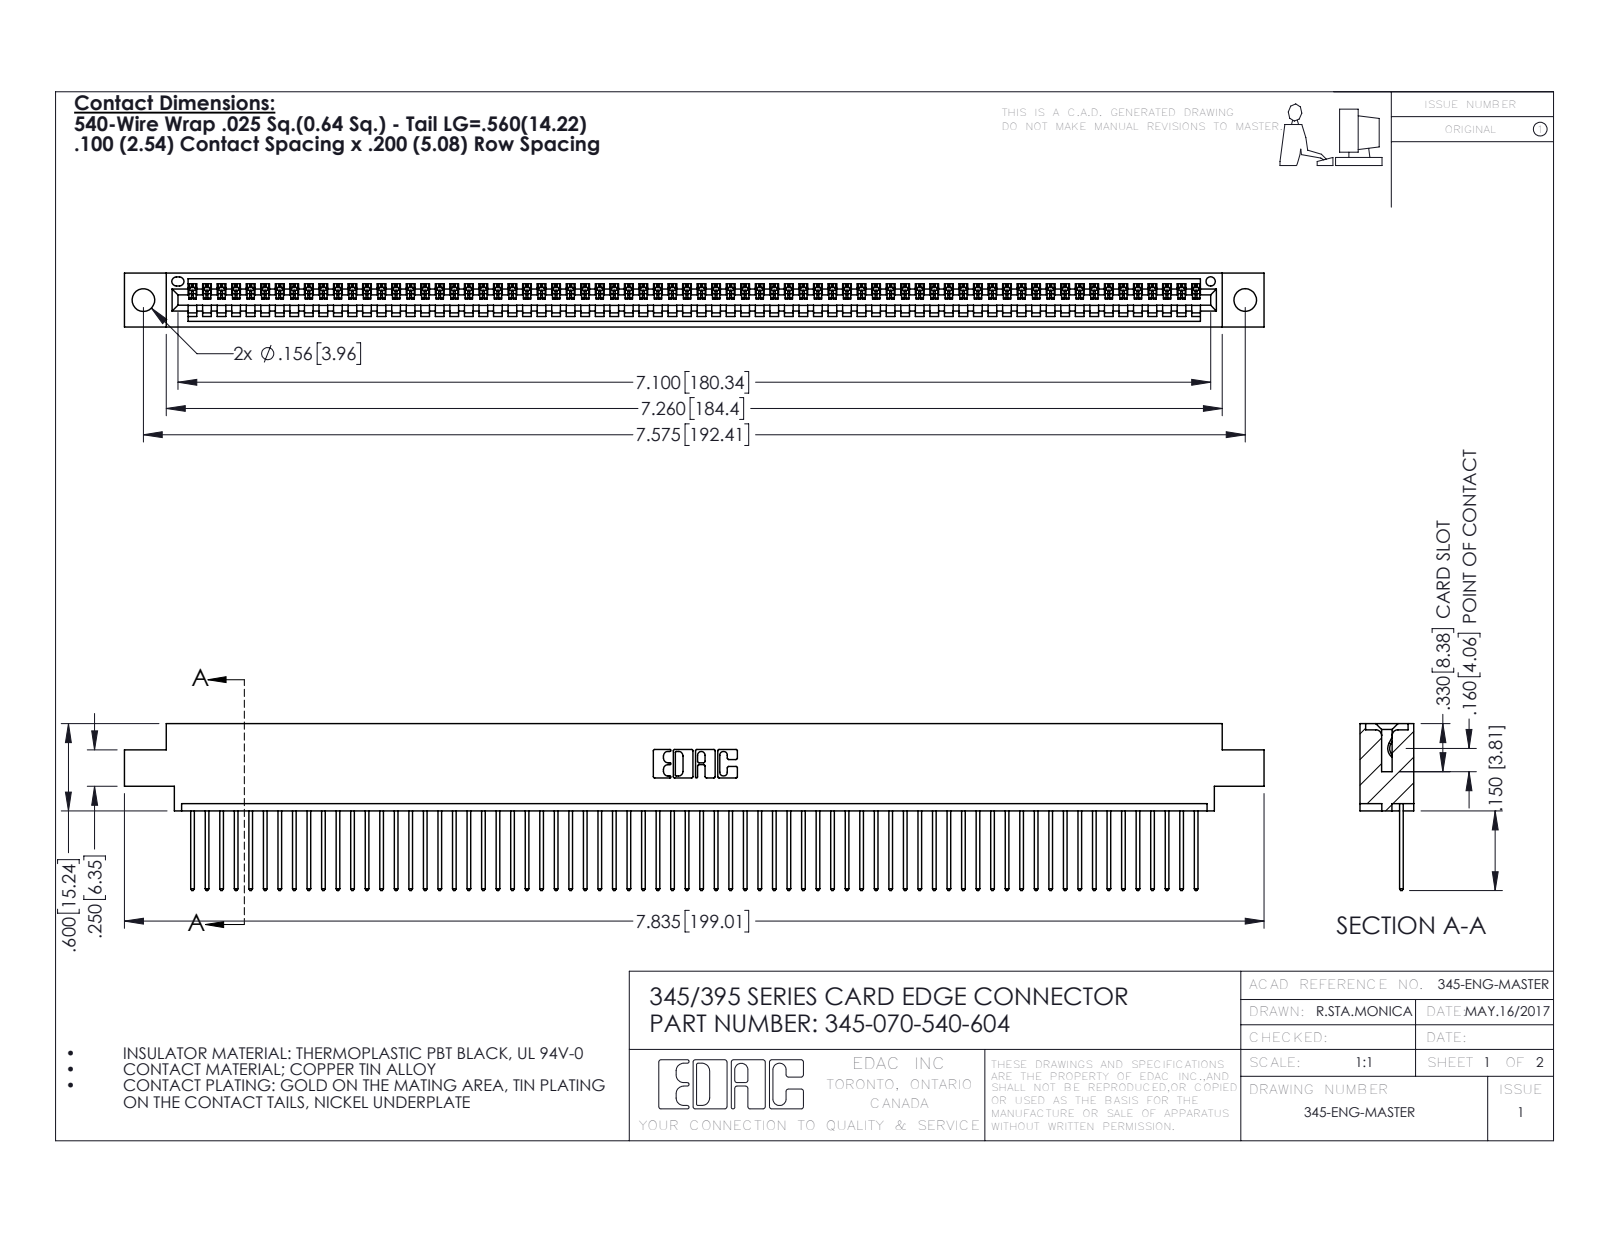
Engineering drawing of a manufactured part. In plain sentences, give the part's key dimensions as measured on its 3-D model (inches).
The part is named "345 Part_0.170 Offset - 0.156 Dia-TH; 345-070-540-604; 345-292-001_345-293-140". Its 3-D file was written by "SolidWorks 2016 (CONFIG_CONTROL_DESIGN)". It is 71 solids with 4190 faces: 2884 planar, 1306 cylindrical and 0 other. Overall it measures 7.835 by 1.147 by 0.37 inches. Its volume is 1.161 cubic inches and its surface area 40.73 square inches. Round holes: 2 of diameter 0.156, 1 of diameter 0.064. Partial cylindrical surfaces (rounded edges, fillets, slot ends): 140 of radius 0.006, 140 of radius 0.01, 22 of radius 0.01, 6 of radius 0.007, 6 of radius 0.031, 3 of radius 0.026, 2 of radius 0.031, 2 of radius 0.04. The main face-to-face distances are 0.072, 0.298, 0.37, 0.098, 0.272, 0.025, 0.2, 0.225, 0.175, 0.149. The hole center spacings are 0.27, 7.339, 7.575.
